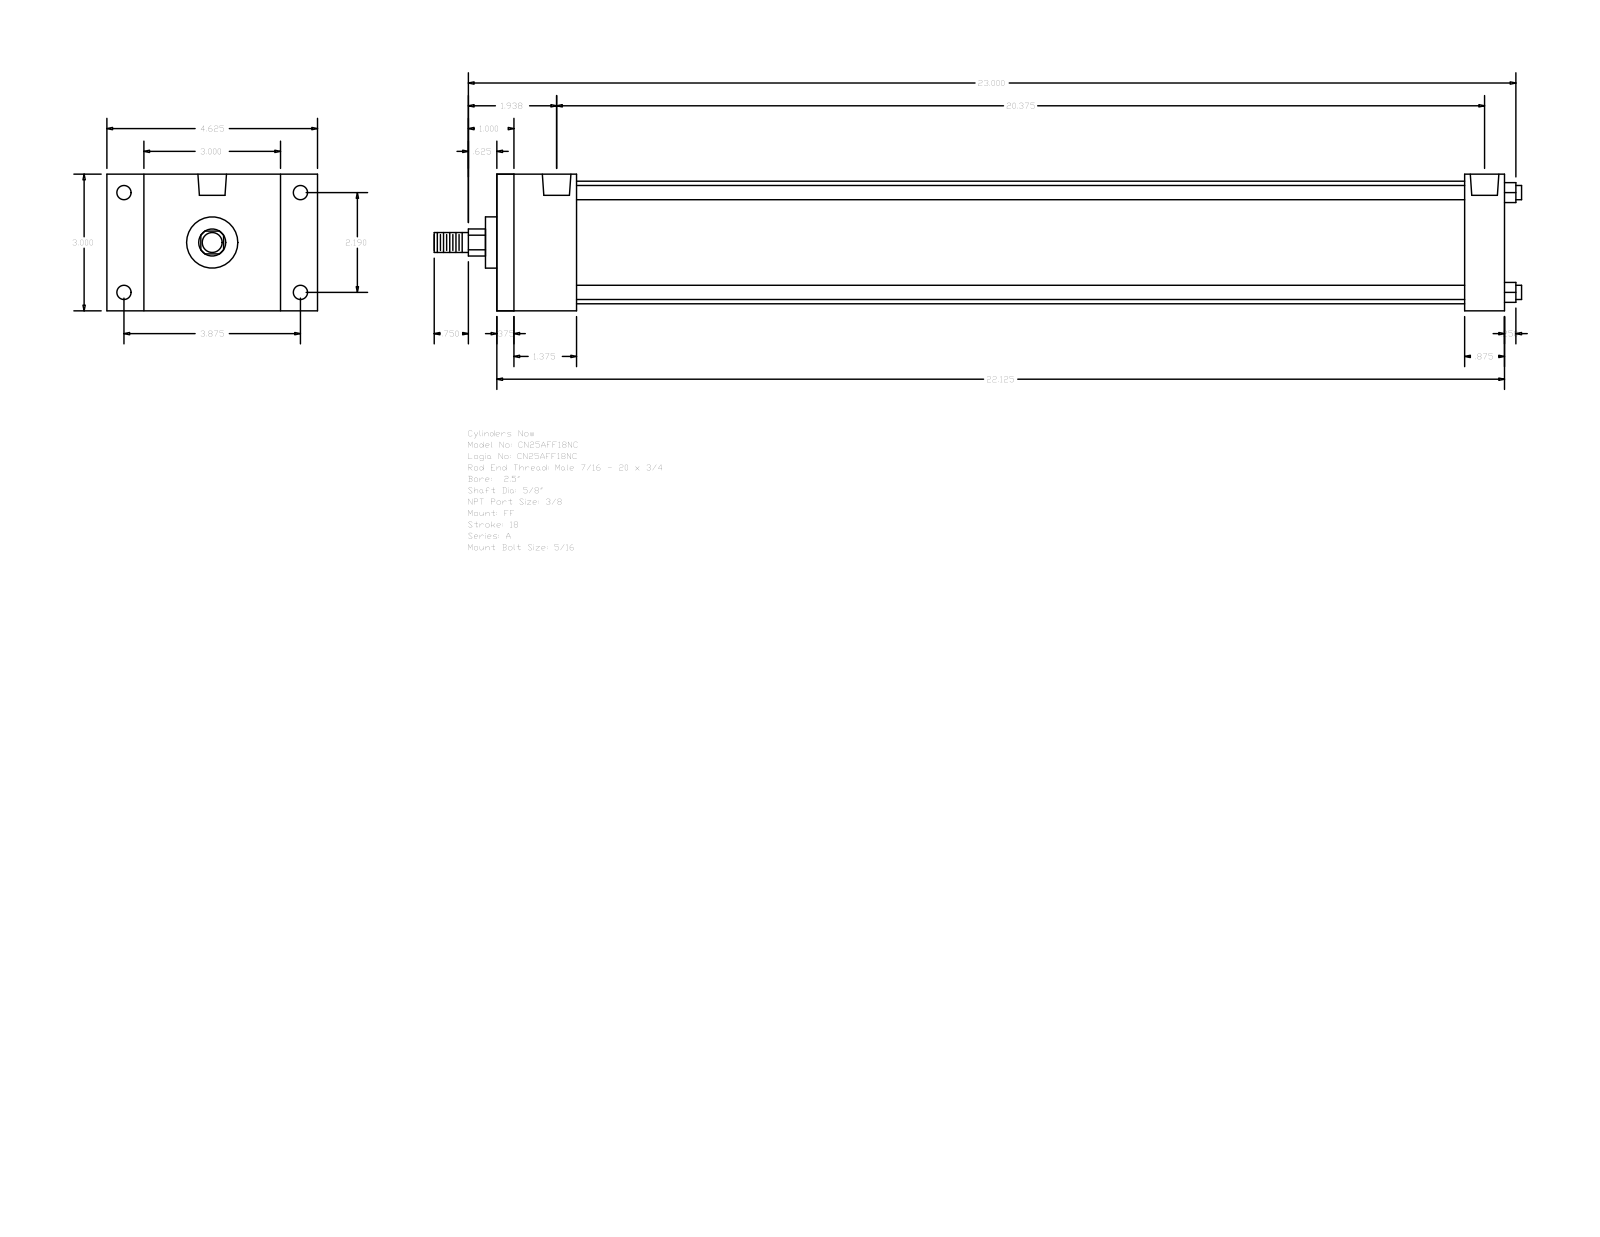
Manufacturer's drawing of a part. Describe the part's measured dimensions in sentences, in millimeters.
The part is named "A_FF__0250_0.625". Its 3-D file was written by "GSSL Pune (CONFIG_CONTROL_DESIGN)". It is 0 solids with 92 faces: 64 planar, 28 cylindrical and 0 other. Overall it measures 606.42 by 117.47 by 76.2 millimeters. Round holes: 4 of diameter 5.56, 4 of diameter 7.94, 2 of diameter 15.93. Round bosses or shafts: 4 of diameter 7.94, 1 of diameter 68.33, 1 of diameter 28.57, 1 of diameter 15.88, 1 of diameter 11.11. Partial cylindrical surfaces (rounded edges, fillets, slot ends): 1 of radius 7.54. The main face-to-face distances are 76.2, 561.97, 9.52, 552.45, 44.45, 34.93, 539.74, 530.22, 495.29, 517.52. The hole center spacings are 2.38, 55.62, 98.42, 113.05, 519.91, 522.29, 517.53.
